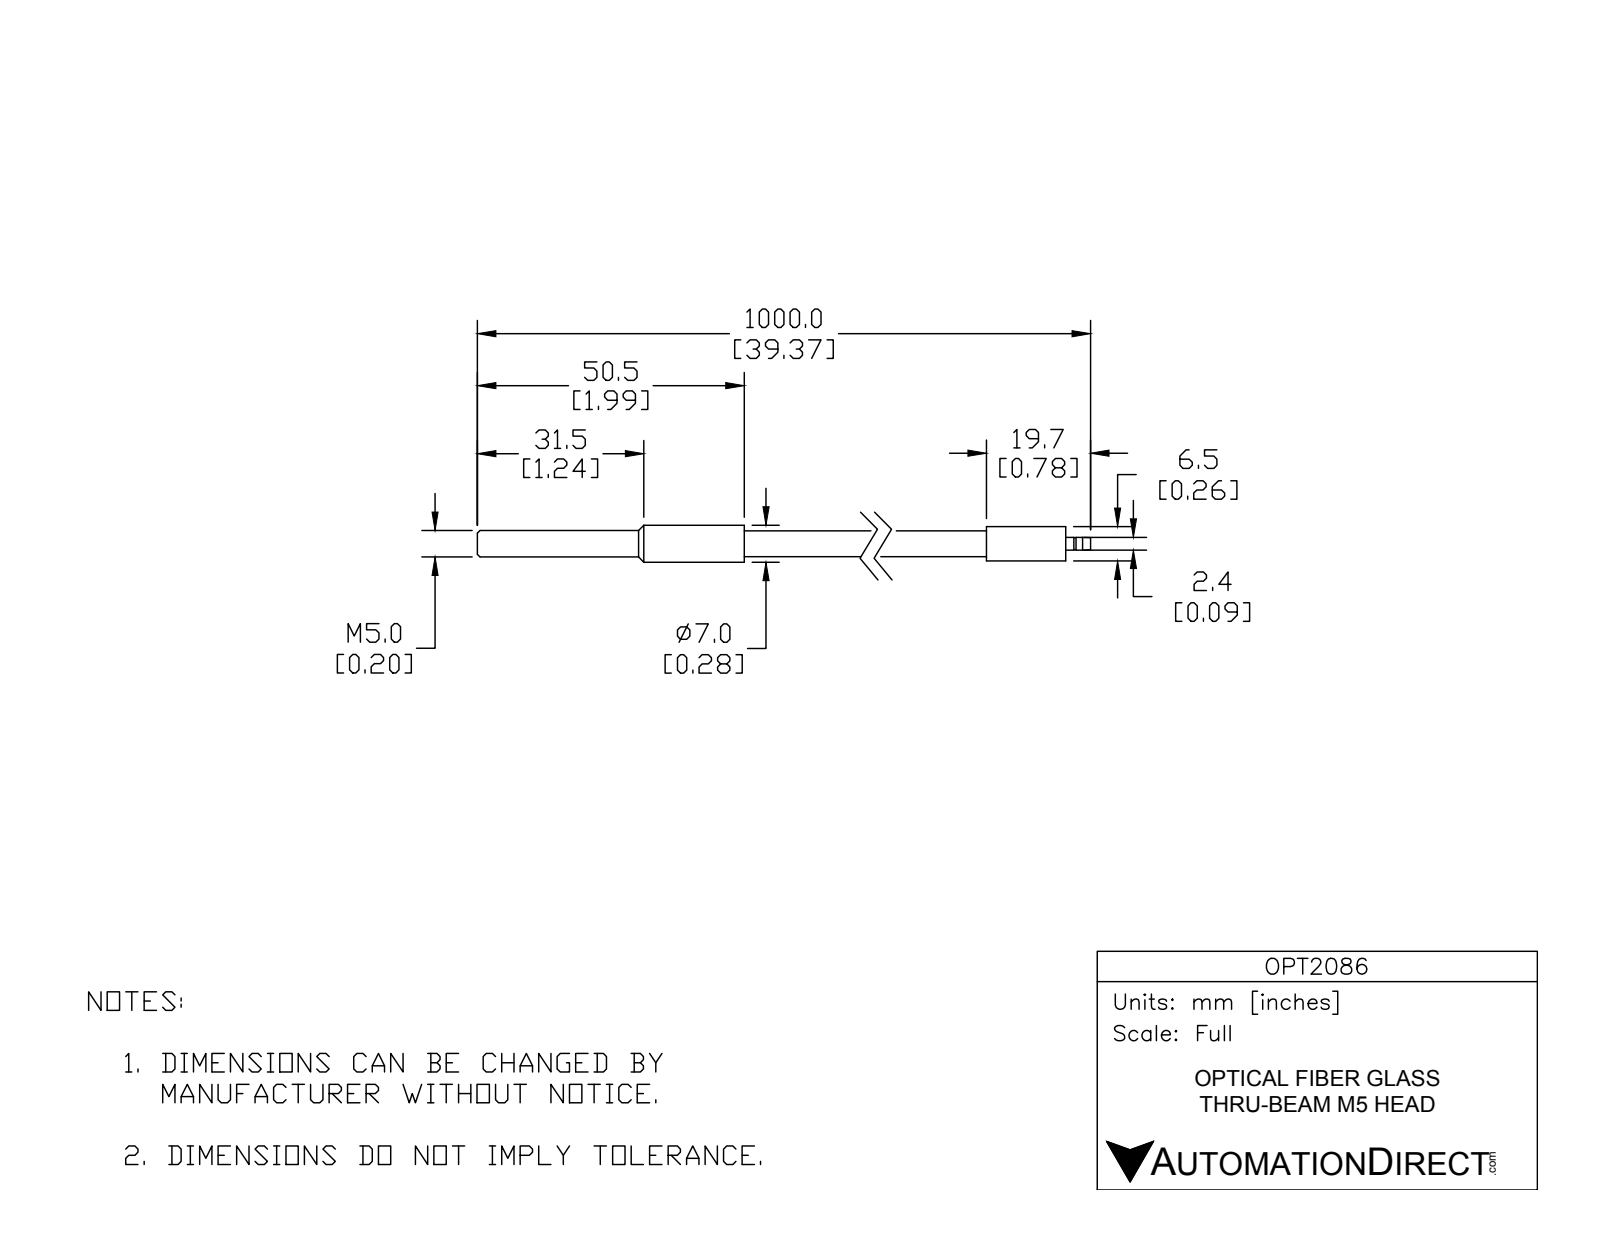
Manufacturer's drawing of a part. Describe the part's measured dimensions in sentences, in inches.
The part is named "OPT2086". Its 3-D file was written by "SolidWorks 2014 (AUTOMOTIVE_DESIGN)". It is 1 solid with 27 faces: 5 planar, 12 cylindrical and 10 other. Overall it measures 39.37 by 0.276 by 0.276 inches. Its volume is 1.184 cubic inches and its surface area 24.27 square inches. Round bosses or shafts: 1 of diameter 0.276, 1 of diameter 0.256, 1 of diameter 0.197, 1 of diameter 0.193, 1 of diameter 0.094. The main face-to-face distances are 37.197, 36.606, 0.591, 1.988, 38.594, 39.185, 39.37, 37.382, 0.776, 0.185.
